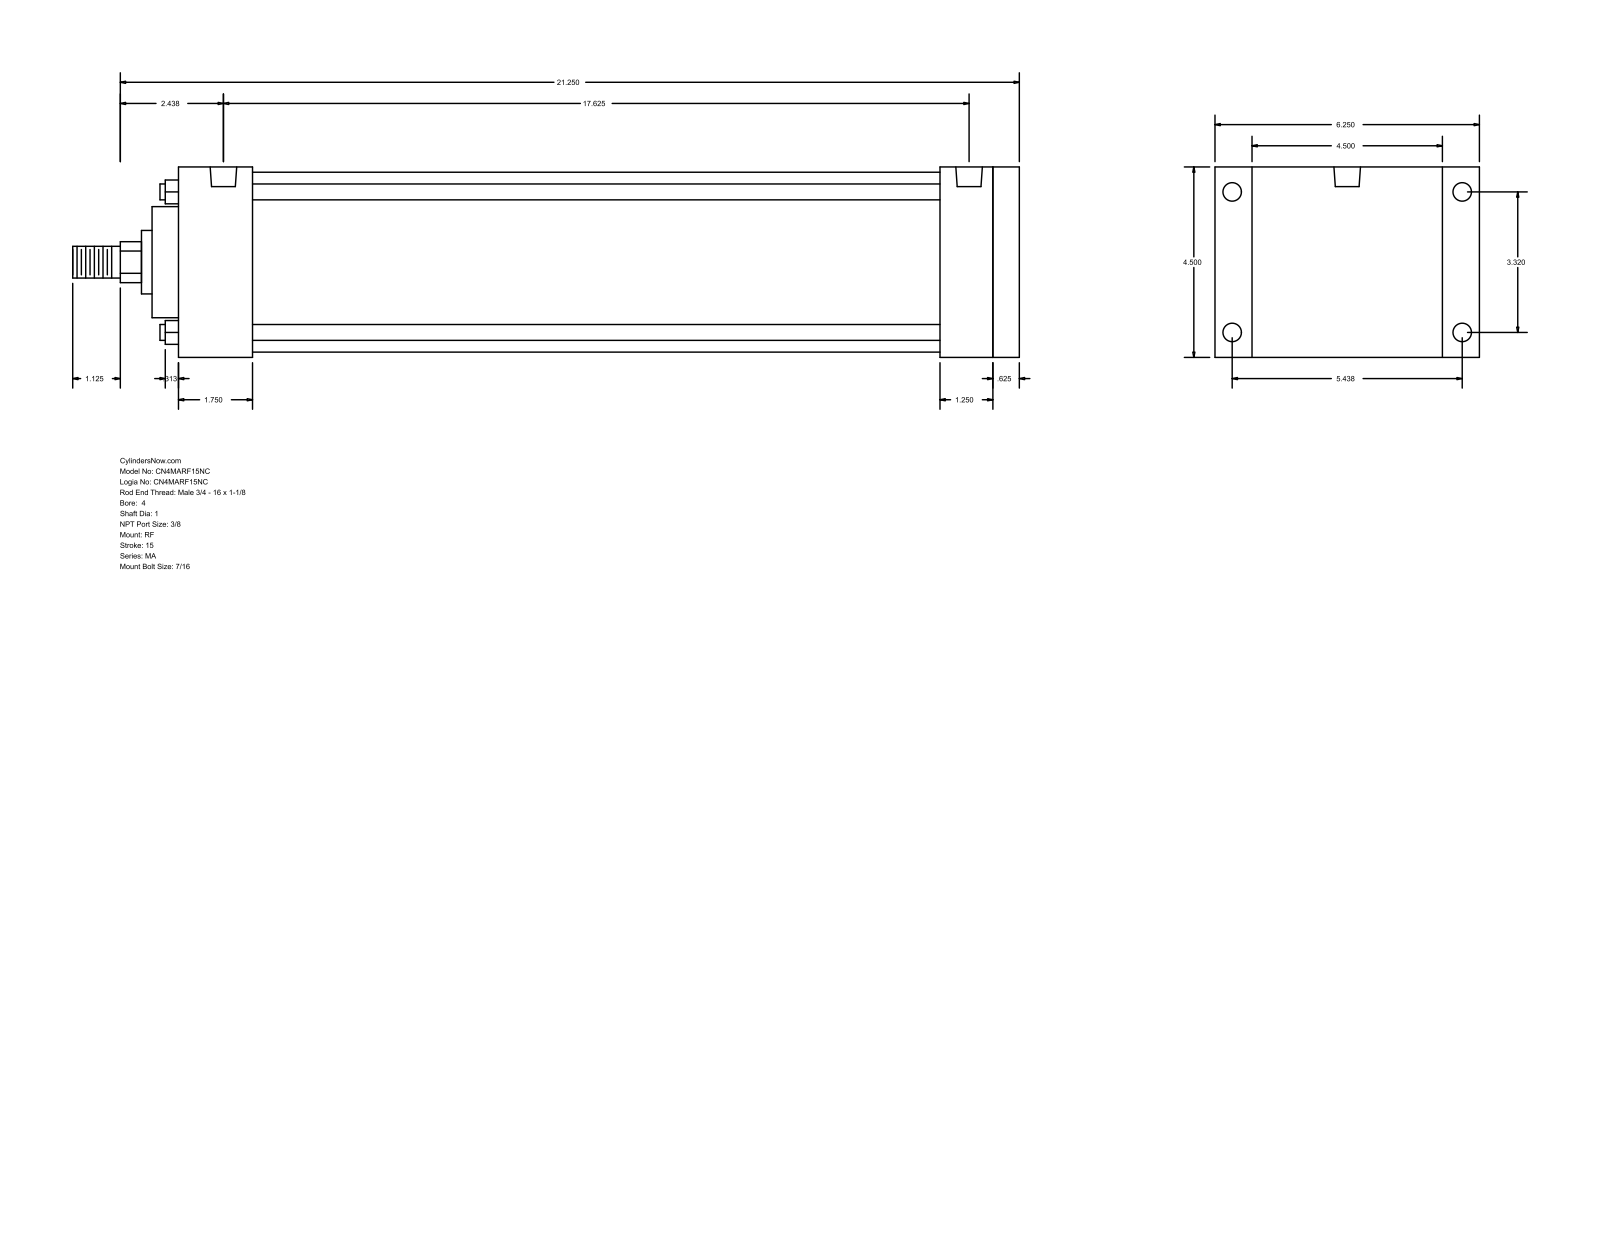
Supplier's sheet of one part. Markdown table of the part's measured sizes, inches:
| quantity | value |
| --- | --- |
| part name | MA_RF__0400_1 |
| STEP written by | GSSL Pune (CONFIG_CONTROL_DESIGN) |
| units | inches |
| bodies | 0 solids, 94 faces (65 planar, 29 cylindrical, 0 other) |
| overall size | 22.375 × 6.25 × 4.5 |
| round holes (diameter × count) | 0.437 × 8, 0.627 × 2 |
| round bosses / shafts (diameter × count) | 0.375 × 4, 4.25 × 1, 2.625 × 1, 1.5 × 1, 1 × 1, 0.75 × 1 |
| partial cylindrical surfaces (radius × count) | 0.484 × 1 |
| main face-to-face distances | 4.5, 19.875, 0.625, 19.25, 0.875, 5.375, 18, 1.25, 1.875, 1.75 |
| hole center spacings | 3.32, 5.438, 6.371, 17.25, 0.187, 0.188, 17.437, 17.438 |
